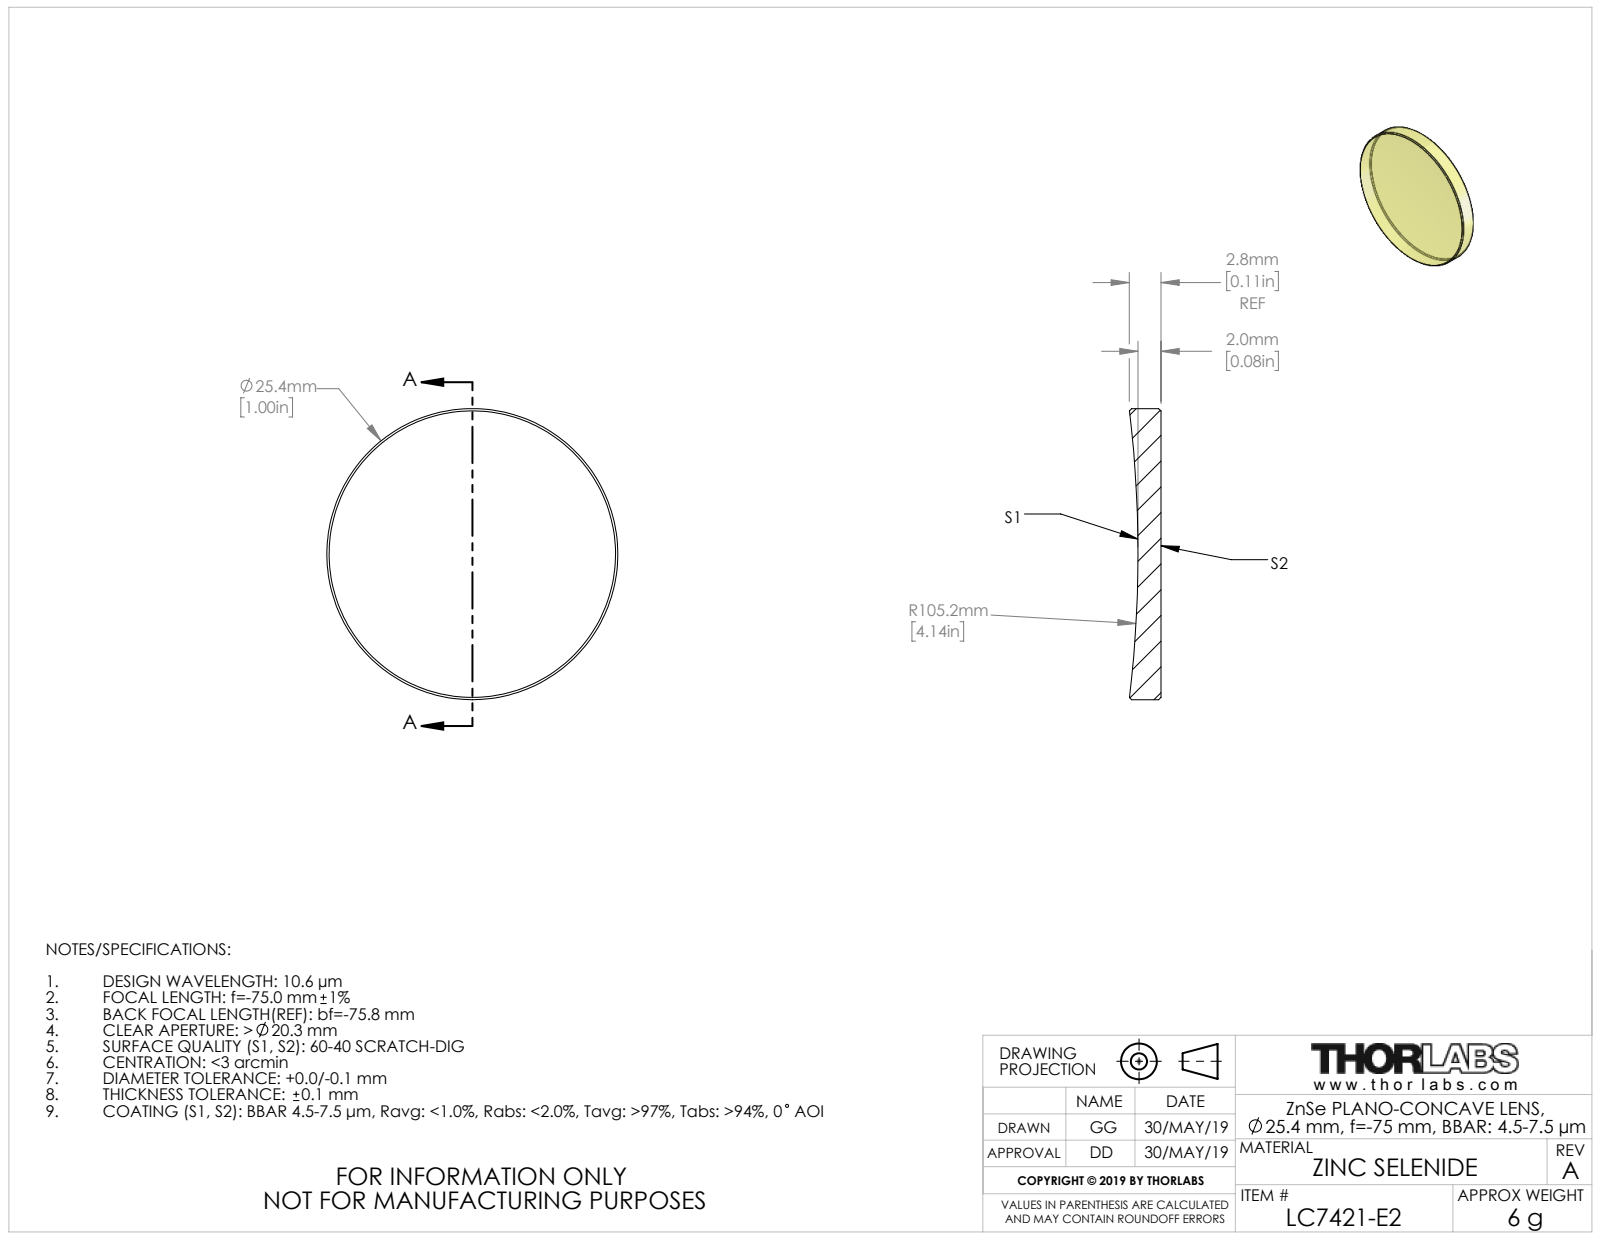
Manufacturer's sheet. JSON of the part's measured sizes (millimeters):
{"part_name": "TTN047633-E0W", "step_written_by": "SolidWorks 2018 (CONFIG_CONTROL_DESIGN)", "units": "millimeters", "bodies": {"solids": 1, "faces": 9, "planar": 1, "cylindrical": 2, "other": 6}, "overall_size": [25.4, 25.4, 2.75], "volume_mm3": 1205, "surface_area_mm2": 1216, "round_bosses_or_shafts": [[25.4, 1]]}
